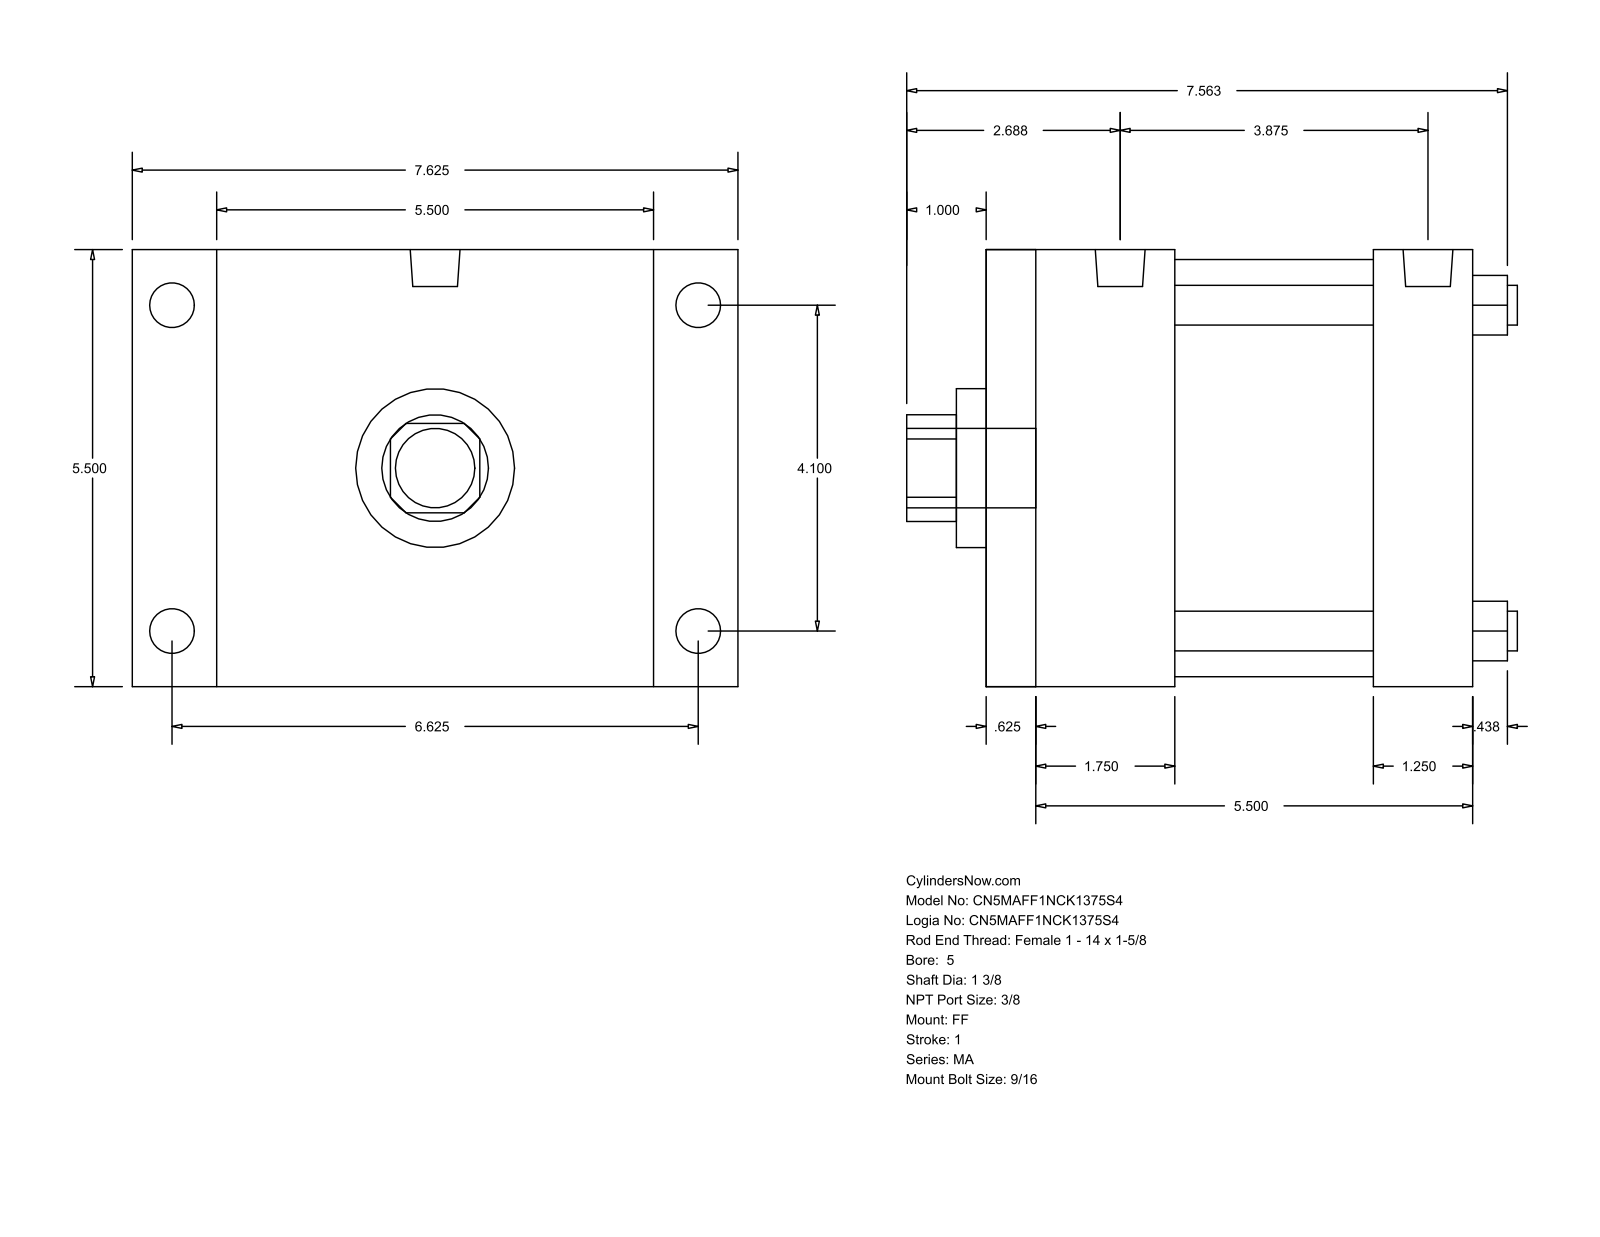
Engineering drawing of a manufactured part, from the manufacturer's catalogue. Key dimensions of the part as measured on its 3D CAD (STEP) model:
Part name (STEP PRODUCT): MA_FF__0500_1.375
STEP written by: GSSL Pune (CONFIG_CONTROL_DESIGN)
Units: millimetres
Bodies: 0 solids, 92 faces (64 planar, 28 cylindrical, 0 other)
Overall size (bounding box): 195.26 × 193.68 × 139.7
Round holes (diameter × count): ⌀12.7 ×4, ⌀34.92 ×1, ⌀50.8 ×1, ⌀133.35 ×1
Round bosses / shafts (diameter × count): ⌀14.29 ×4, ⌀11.11 ×4, ⌀15.93 ×2, ⌀25.4 ×1
Partial cylindrical surfaces — rounded edges, fillets, slot ends (radius × count): R17.06 ×1
Main face-to-face distances: 139.7, 155.57, 15.87, 166.69, 123.82, 107.95, 31.75, 60.32, 44.45, 63.5
Hole centre spacings: 73.64, 104.14, 147.28
